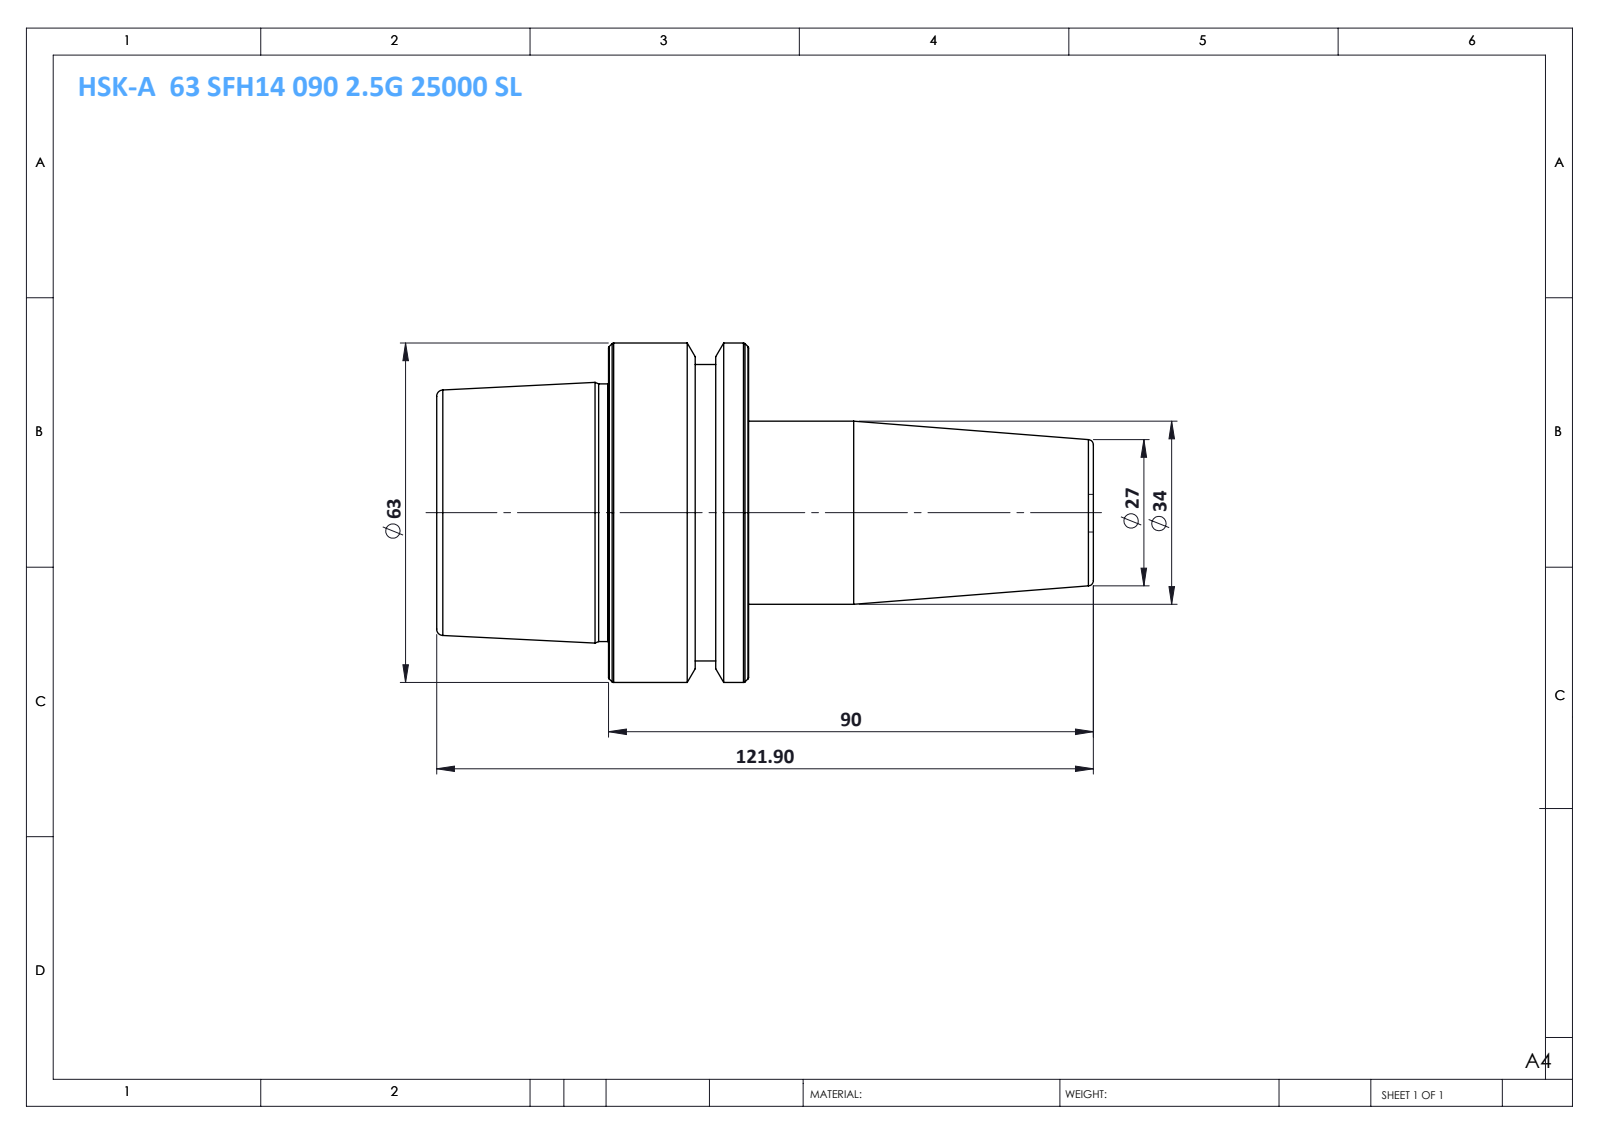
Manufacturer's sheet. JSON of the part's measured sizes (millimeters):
{"part_name": "HSK-A 63 SFH14 090 2.5G 25000 SL", "step_written_by": "SolidWorks 2014 (CONFIG_CONTROL_DESIGN)", "units": "millimeters", "bodies": {"solids": 1, "faces": 46, "planar": 6, "cylindrical": 10, "other": 30}, "overall_size": [121.9, 63, 63], "volume_mm3": 182946, "surface_area_mm2": 22643, "round_bosses_or_shafts": [[63, 1], [55, 1], [47.78, 1], [34, 1]], "face_to_face_distances": [57.9, 26, 31.9, 64, 90, 121.9, 70.1, 6.1, 19.9, 51.8]}
